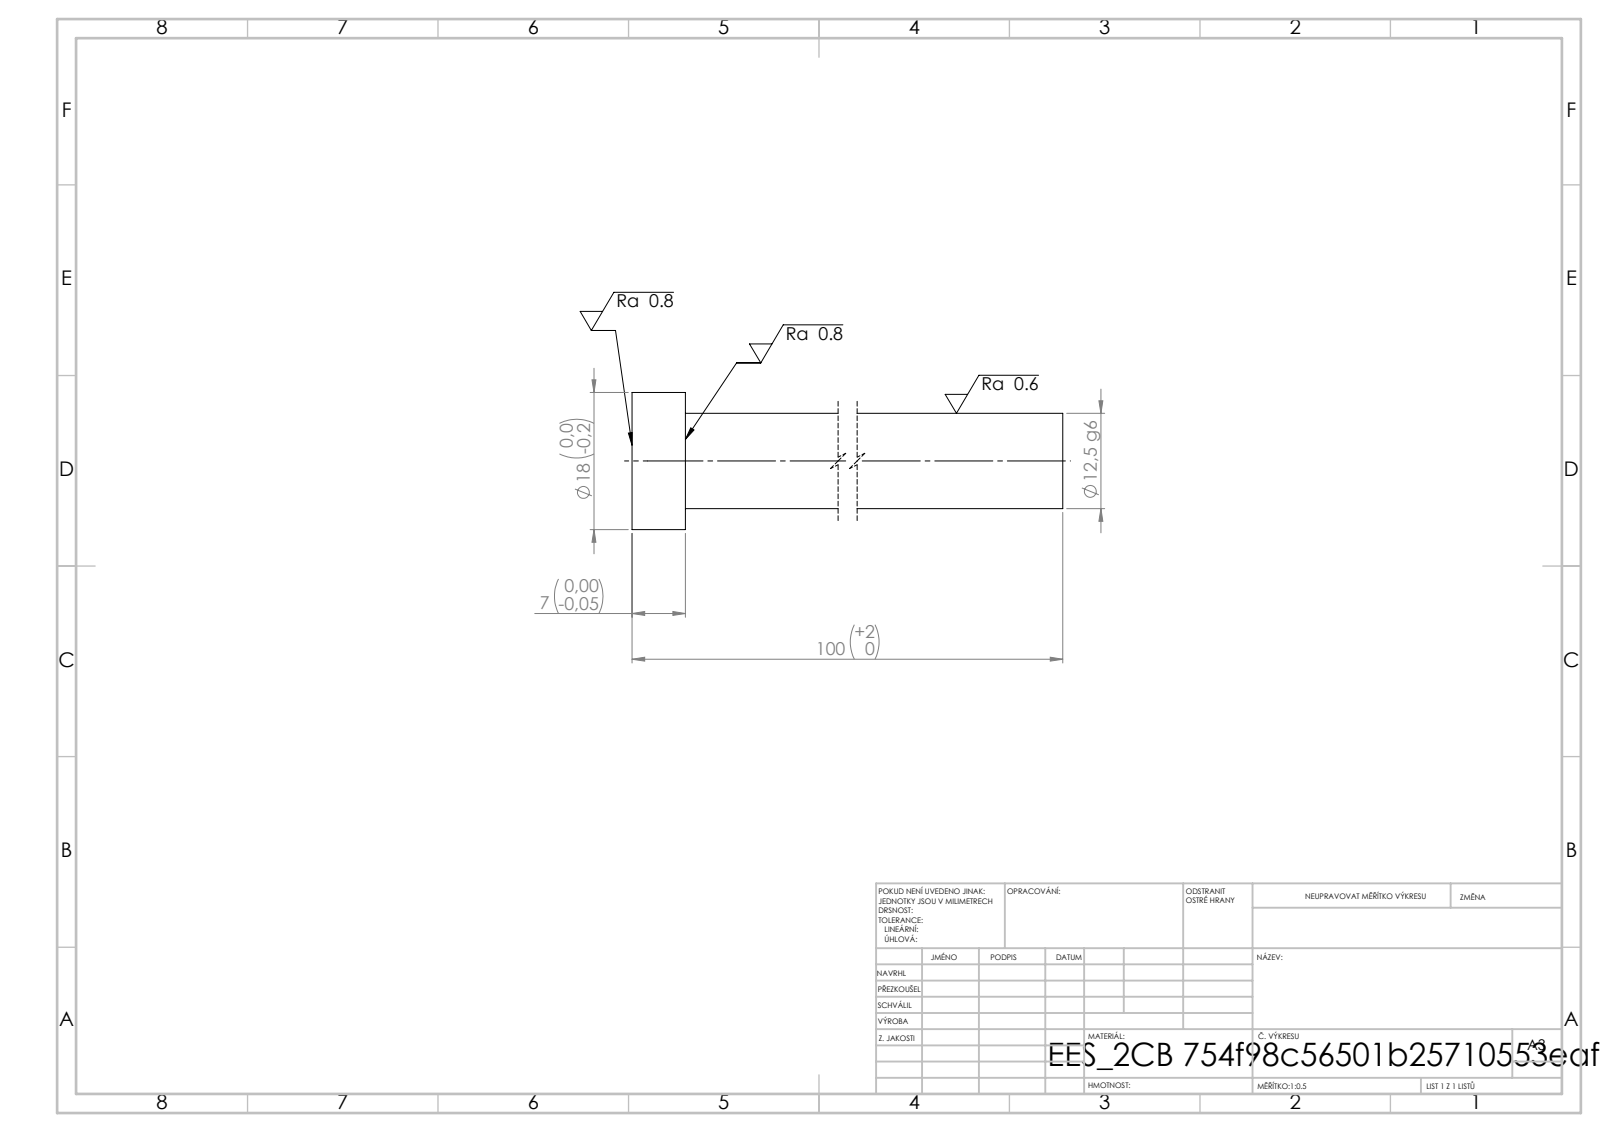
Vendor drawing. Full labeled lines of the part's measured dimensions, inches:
STEP written by: SolidWorks 2019 (CONFIG_CONTROL_DESIGN)
Units: inches
Bodies: 1 solid, 7 faces (3 planar, 4 cylindrical, 0 other)
Overall size (bounding box): 3.937 × 0.709 × 0.709
Volume: 0.805 in³ · Surface area: 7.063 in²
Round bosses / shafts (diameter × count): ⌀0.709 ×1, ⌀0.492 ×1
Main face-to-face distances: 0.276, 3.937, 3.661
